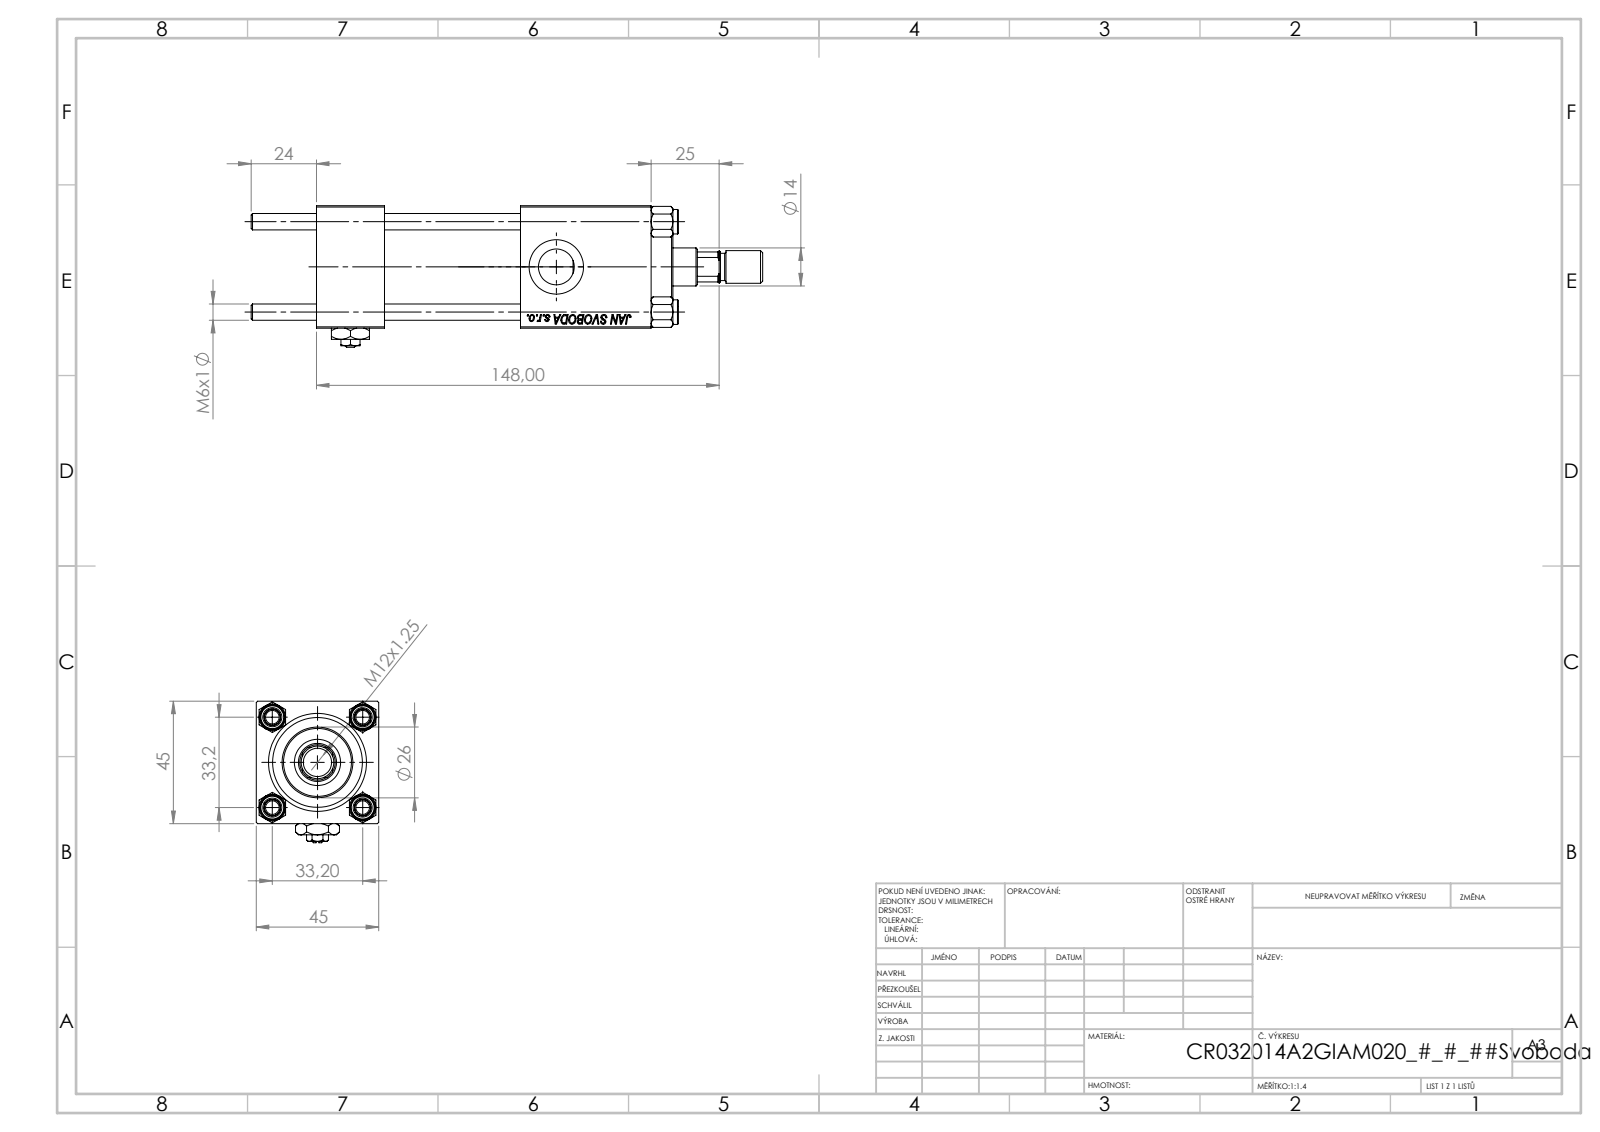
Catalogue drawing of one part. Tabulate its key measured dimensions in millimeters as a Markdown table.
| quantity | value |
| --- | --- |
| part name | ROD_END_AH; NUT_M5; V215CR_VCP; V215_VC_A (+3 more) |
| STEP written by | SolidWorks 2019 (CONFIG_CONTROL_DESIGN) |
| units | millimeters |
| bodies | 13 solids, 1198 faces (546 planar, 88 cylindrical, 564 other) |
| overall size | 188 × 52 × 45 |
| volume | 199 191 mm³ |
| surface area | 74 744 mm² |
| round holes (diameter × count) | 6 × 4, 7 × 2, 13.16 × 2, 20 × 2, 6.5 × 1, 14 × 1, 17 × 1, 24 × 1, 32 × 1, 33 × 1 |
| round bosses / shafts (diameter × count) | 9 × 4, 38 × 1, 26 × 1, 12 × 1, 10 × 1 |
| partial cylindrical surfaces (radius × count) | 6.5 × 1 |
| main face-to-face distances | 45, 25, 123, 98, 50, 75, 48, 94.3, 69.3, 19.3 |
| hole center spacings | 23.48, 33.2, 46.95 |
